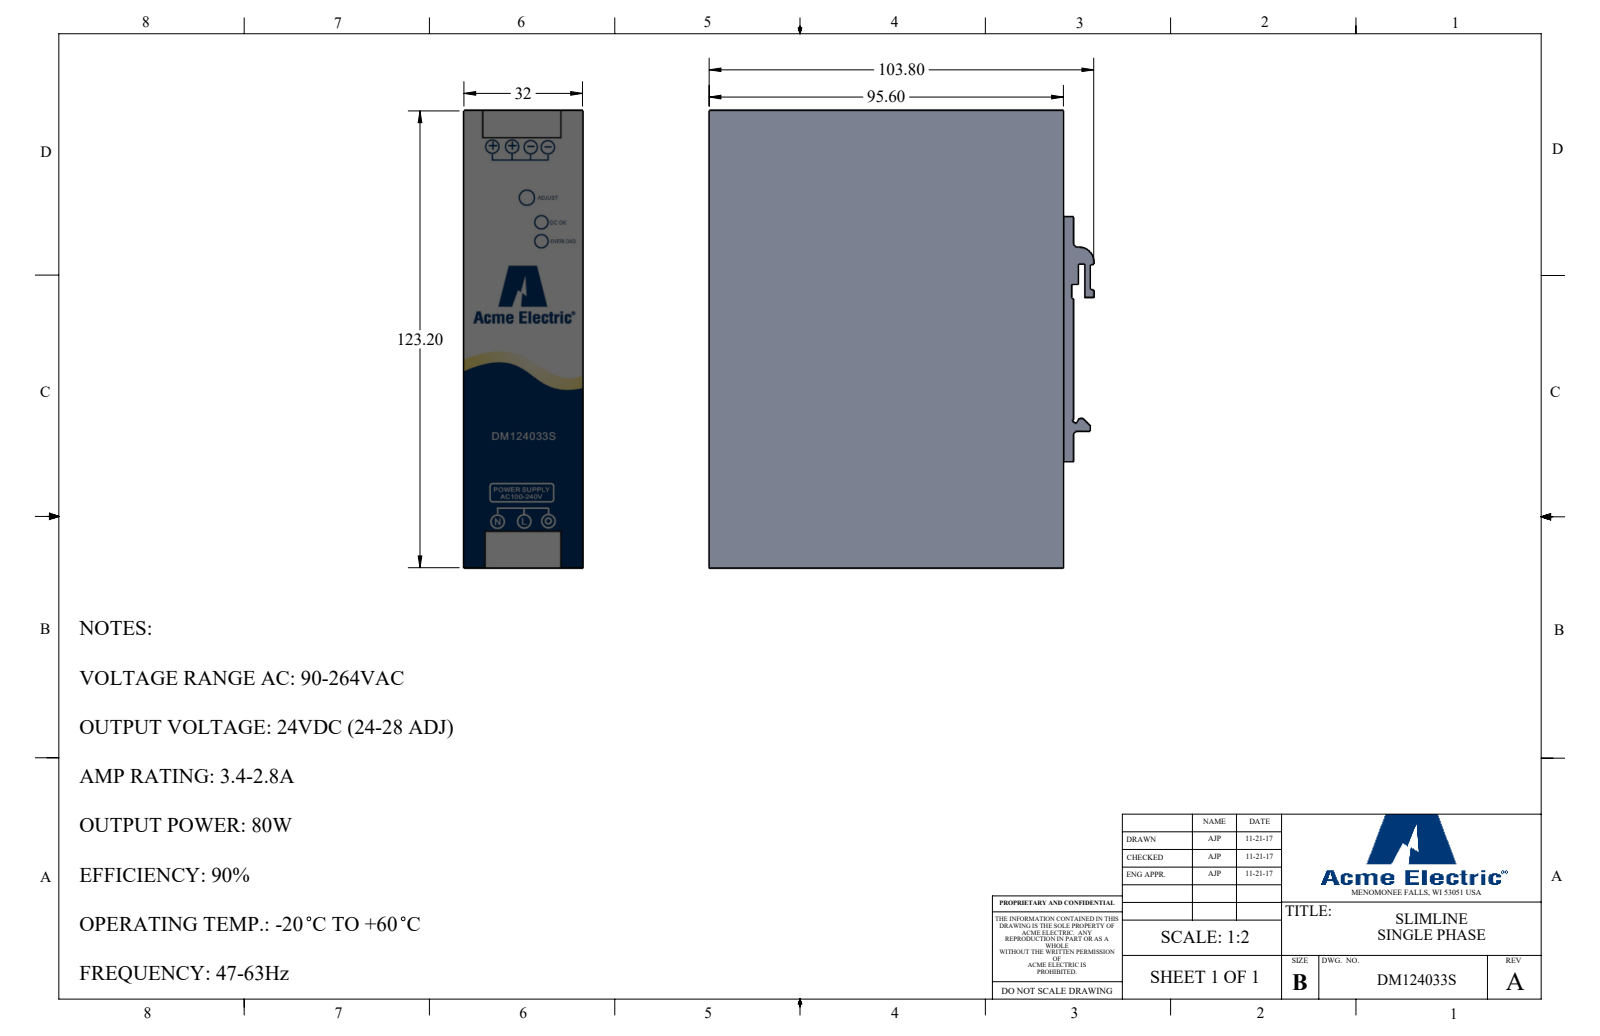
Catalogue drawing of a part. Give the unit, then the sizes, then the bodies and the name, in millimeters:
Units: millimetres
Overall size (bounding box): 123.2 × 103.8 × 32
Partial cylindrical surfaces — rounded edges, fillets, slot ends (radius × count): R1 ×2, R4 ×1
Main face-to-face distances: 32, 123.2, 95.6, 2.7, 98.3, 1.07, 30.93, 3, 5.7, 101.3
Volume: 383 924 mm³ · Surface area: 39 344 mm²
Bodies: 1 solid, 36 faces (33 planar, 3 cylindrical, 0 other)
Part name (STEP PRODUCT): DM124033S
STEP written by: SolidWorks 2017 (AUTOMOTIVE_DESIGN)
